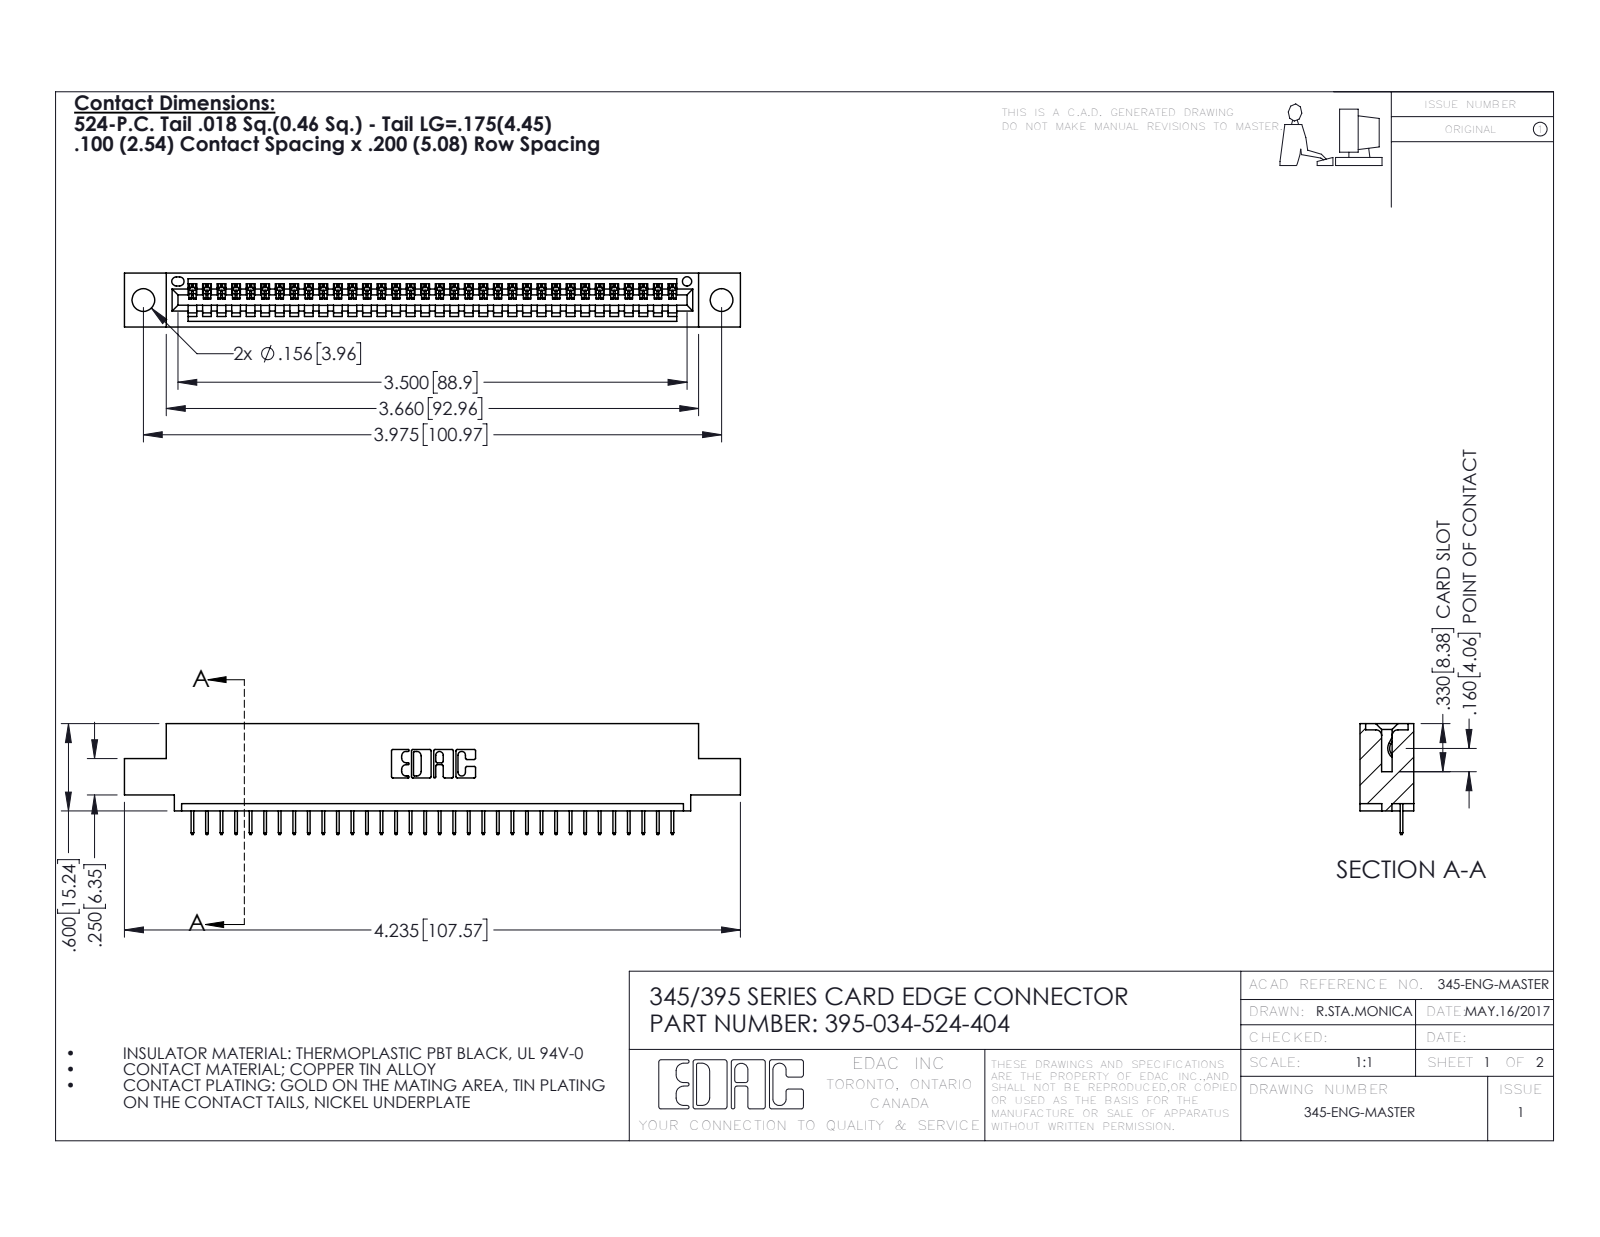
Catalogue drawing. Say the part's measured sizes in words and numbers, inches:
The part is named "395-034-524-404; 345 Part_0.110 Offset - 0.156 Dia-TH; 345-292-001_345-293-124". Its 3-D file was written by "SolidWorks 2016 (CONFIG_CONTROL_DESIGN)". It is 35 solids with 2238 faces: 1648 planar, 590 cylindrical and 0 other. Overall it measures 4.235 by 0.762 by 0.37 inches. Its volume is 0.601 cubic inches and its surface area 19.3 square inches. Round holes: 2 of diameter 0.156, 1 of diameter 0.064. Partial cylindrical surfaces (rounded edges, fillets, slot ends): 68 of radius 0.006, 22 of radius 0.01, 6 of radius 0.007, 6 of radius 0.031, 3 of radius 0.026, 2 of radius 0.031, 2 of radius 0.04, 1 of radius 0.014. The main face-to-face distances are 0.072, 0.298, 0.37, 0.2, 0.098, 0.272, 0.025, 0.225, 0.072, 0.149. The hole center spacings are 0.27, 3.74, 3.975.
